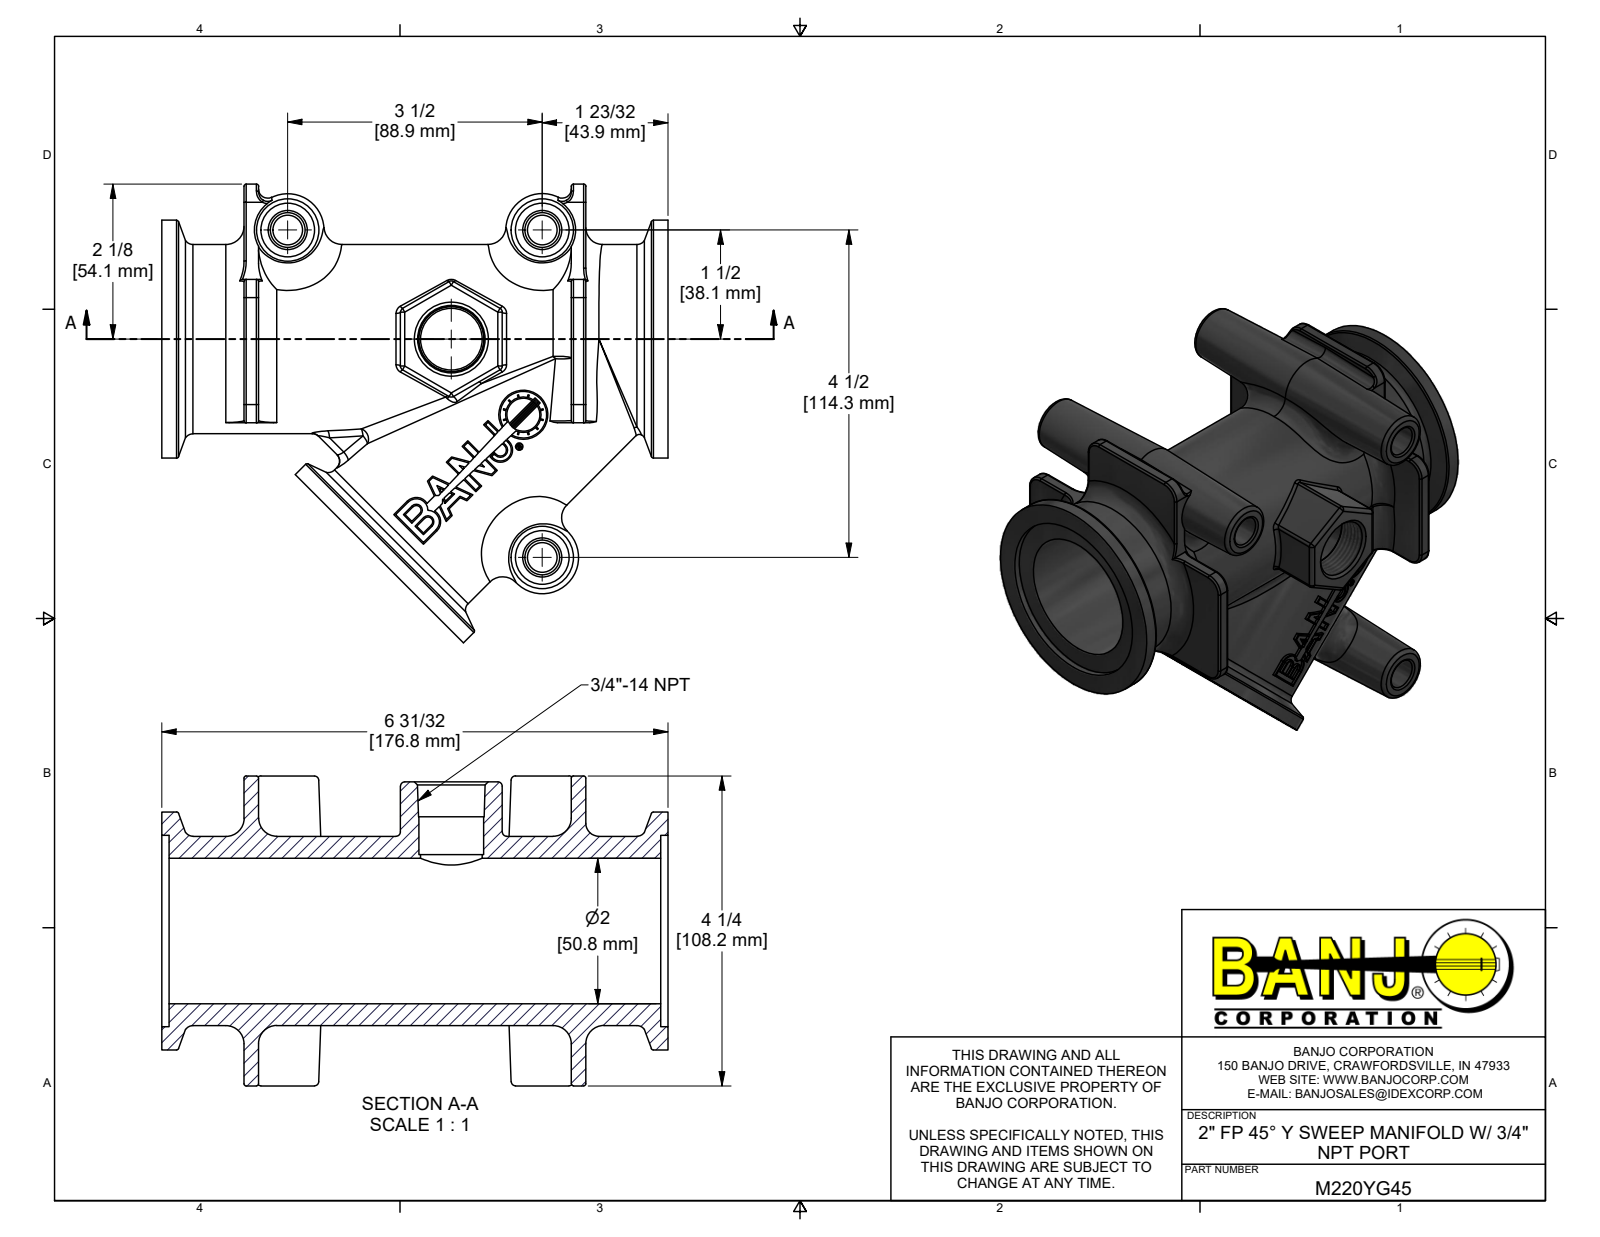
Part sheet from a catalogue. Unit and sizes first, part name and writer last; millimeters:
Units: millimetres
Overall size (bounding box): 176.8 × 160.1 × 108.2
Round holes (diameter × count): ⌀50.8 ×2, ⌀66.8 ×2, ⌀11.5 ×1, ⌀16.3 ×1, ⌀21.5 ×1, ⌀22.6 ×1
Round bosses / shafts (diameter × count): ⌀83.1 ×2, ⌀66 ×2, ⌀17.1 ×1
Partial cylindrical surfaces — rounded edges, fillets, slot ends (radius × count): R0.8 ×24, R1.5 ×12, R6.4 ×6, R1.7 ×2, R2.1 ×2, R3.2 ×2, R4 ×2, R4.4 ×2
Main face-to-face distances: 2.5, 28.7, 148.1, 5.1, 33.8, 143, 114.3, 174.2, 26.2, 31.2
Hole centre spacings: 36.5
Volume: 517 800 mm³ · Surface area: 145 700 mm²
Bodies: 1 solid, 902 faces (413 planar, 172 cylindrical, 317 other)
Part name (STEP PRODUCT): M220YG45; M220YG45X
STEP written by: Autodesk Inventor 2019 (AUTOMOTIVE_DESIGN)
